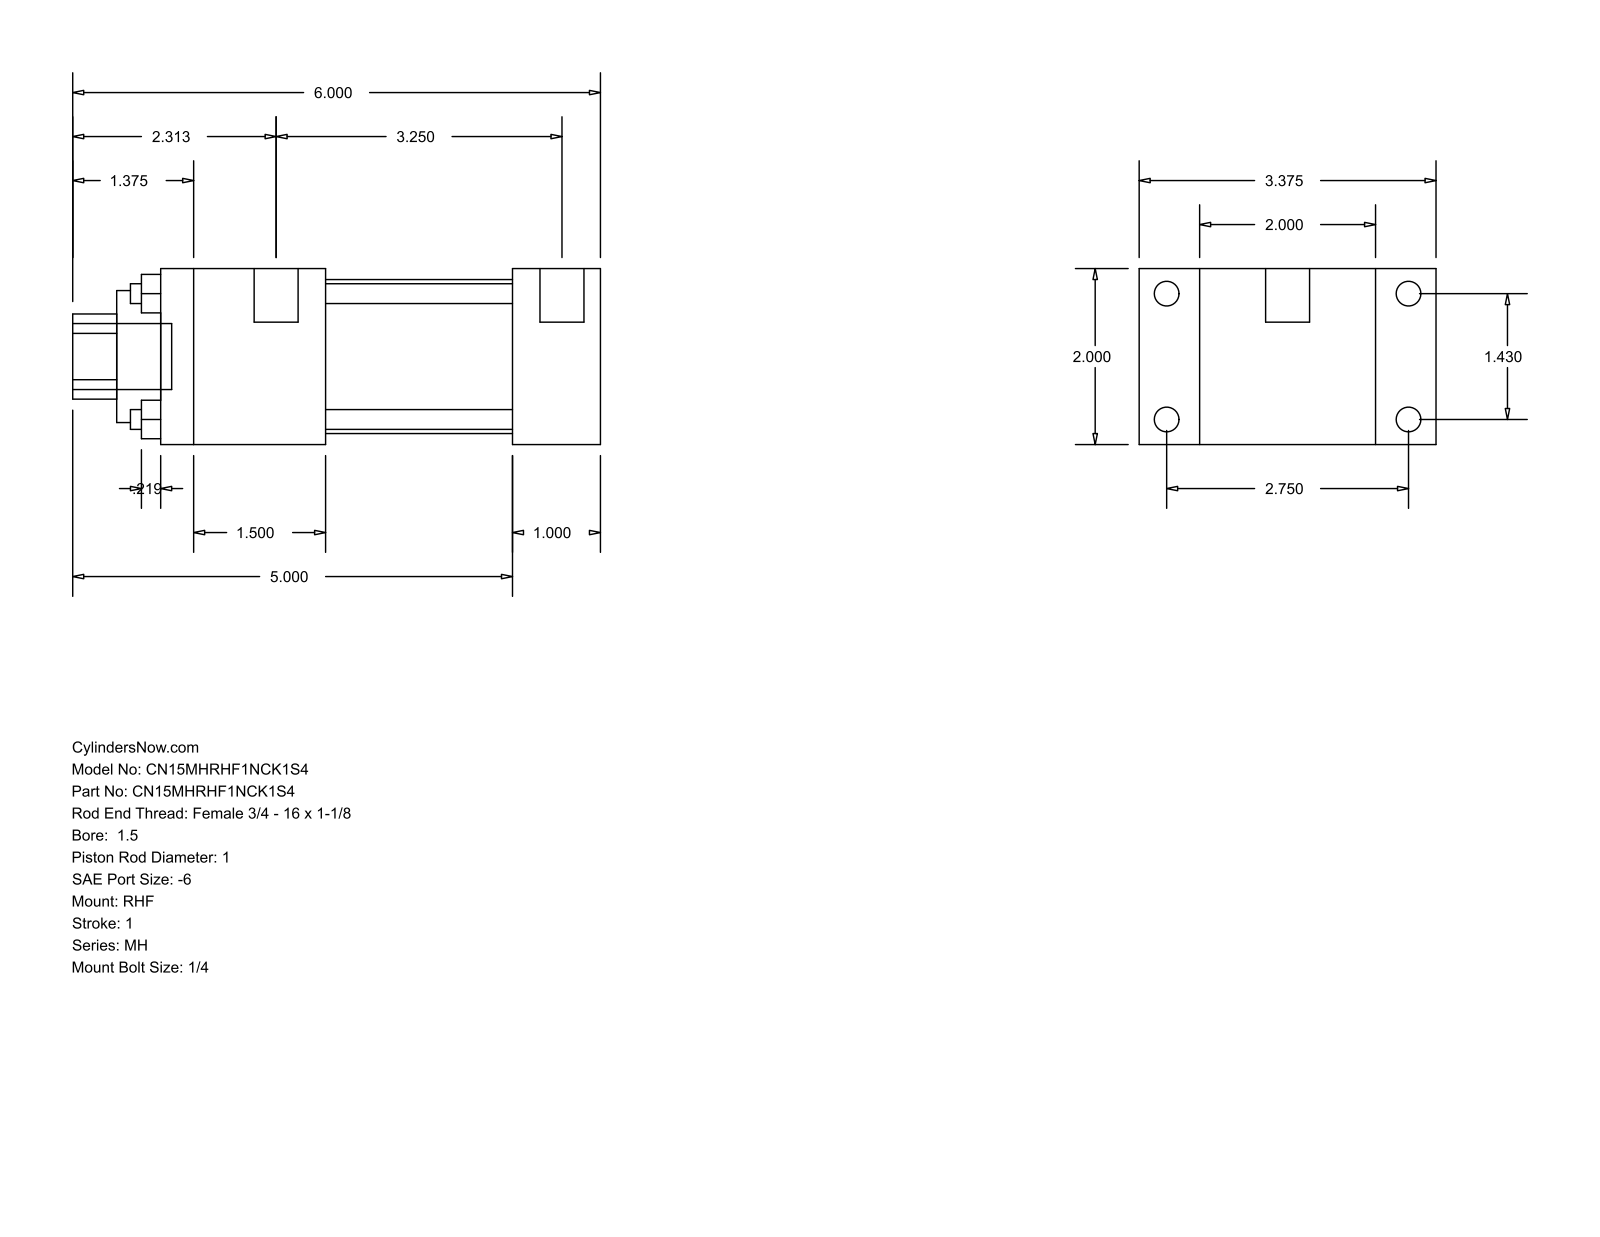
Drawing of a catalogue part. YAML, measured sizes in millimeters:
part_name: "MH_RHF__0150_1"
step_written_by: "GSSL Pune (CONFIG_CONTROL_DESIGN)"
units: millimeters
bodies: {solids: 0, faces: 88, planar: 60, cylindrical: 28, other: 0}
overall_size: [152.4, 85.72, 50.8]
round_holes:
  - {diameter: 5.71, count: 4}
  - {diameter: 25.4, count: 1}
  - {diameter: 38.1, count: 1}
  - {diameter: 44.45, count: 1}
round_bosses_or_shafts:
  - {diameter: 7.14, count: 4}
  - {diameter: 5.56, count: 4}
  - {diameter: 12.7, count: 2}
  - {diameter: 19.05, count: 1}
partial_cylinders:
  - {radius: 12.29, count: 1}
face_to_face_distances: [50.8, 25.4, 17.46, 68.26, 85.72, 127, 101.6, 47.63, 53.97, 79.37]
hole_center_spacings: [25.68, 36.32, 51.36]
